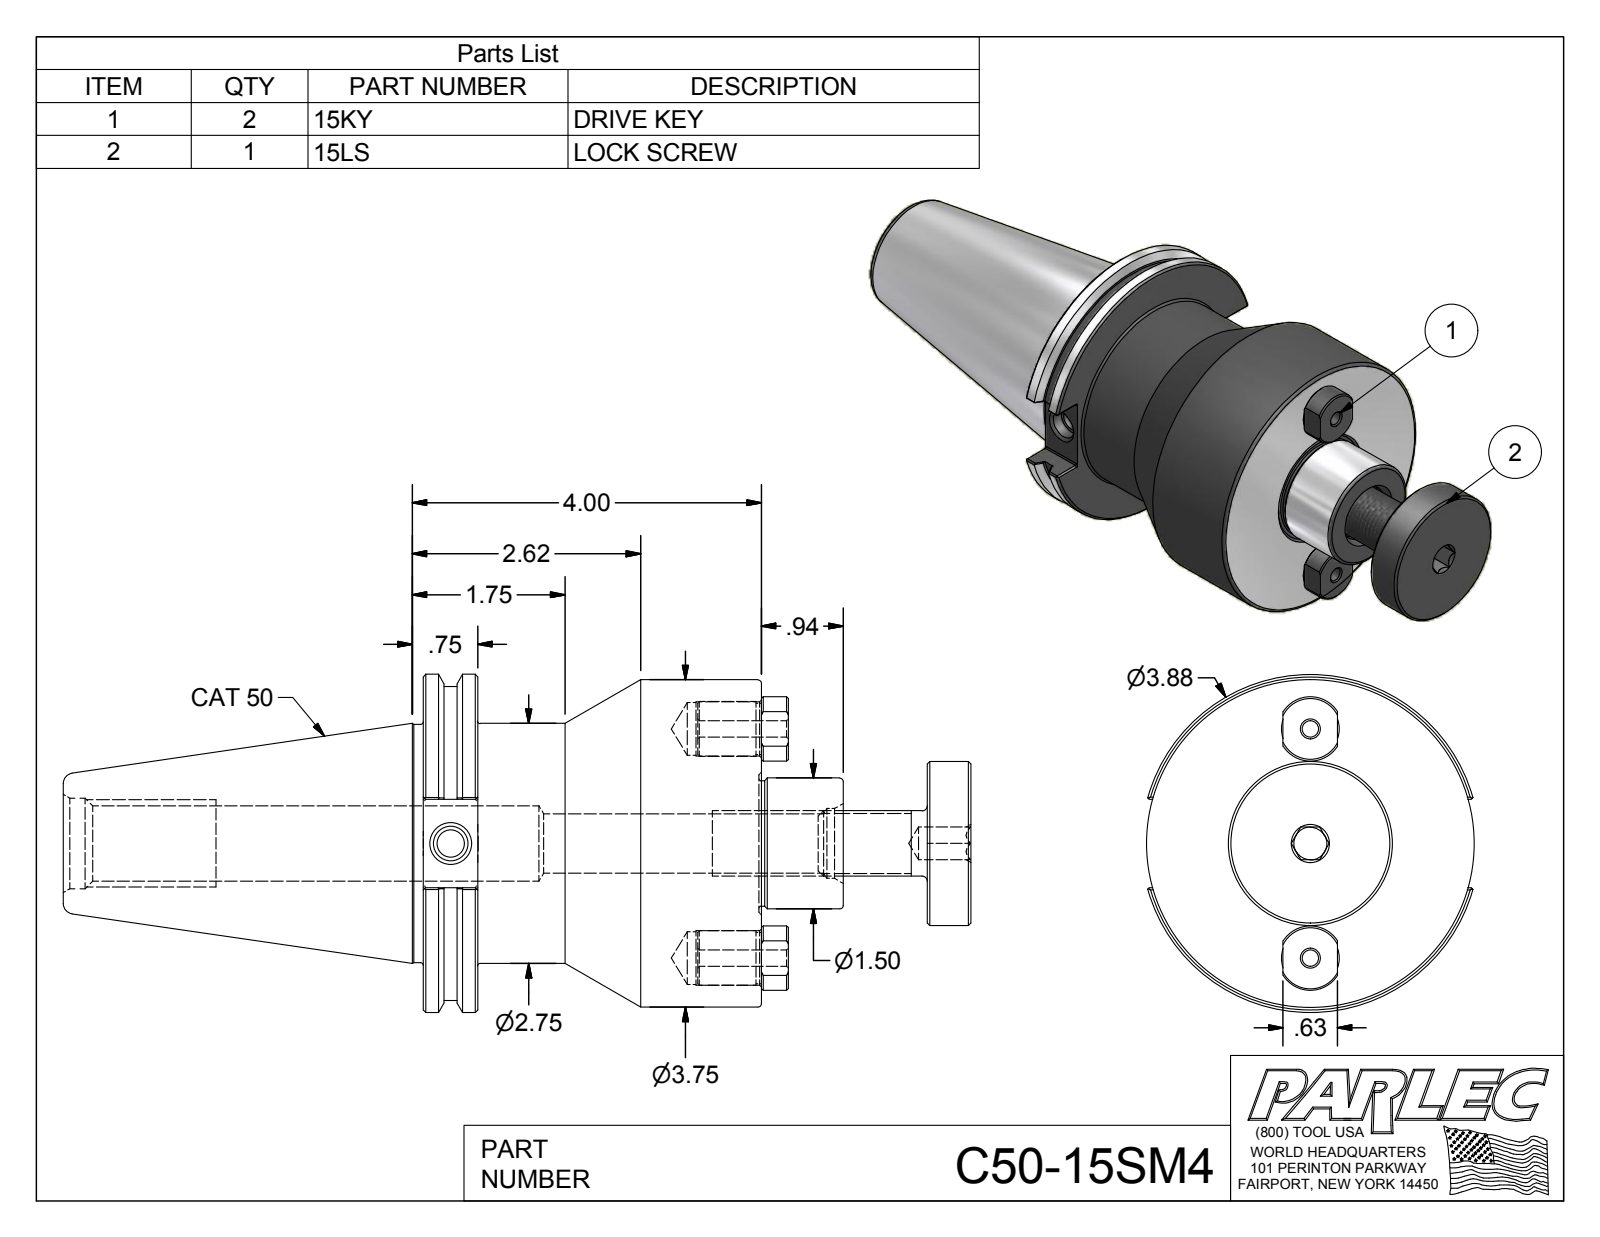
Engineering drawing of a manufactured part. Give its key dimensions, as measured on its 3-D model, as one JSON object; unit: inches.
{"part_name": "C50-15SM4; C50-15SM4-1; 15LS; 15KY", "step_written_by": "Autodesk Inventor 2012 (AUTOMOTIVE_DESIGN)", "units": "inches", "bodies": {"solids": 4, "faces": 166, "planar": 62, "cylindrical": 46, "other": 58}, "overall_size": [10.402, 3.875, 3.75], "volume_in3": 49.68, "surface_area_in2": 144.5, "round_holes": [[0.19, 2], [0.604, 2], [0.624, 2], [0.315, 1], [0.375, 1], [0.399, 1], [0.682, 1], [0.8, 1], [0.865, 1], [1.038, 1]], "round_bosses_or_shafts": [[0.626, 2], [0.59, 2], [3.875, 1], [3.75, 1], [3.594, 1], [2.75, 1], [2.73, 1], [1.88, 1]], "partial_cylinders_radius": [[0.02, 12], [0.37, 2]], "face_to_face_distances": [3.875, 0.625, 3.25, 6.277, 5.652, 2.402, 5.777, 5.152, 1.902, 0.5], "hole_center_spacings": [1.312, 1.312, 2.624]}
